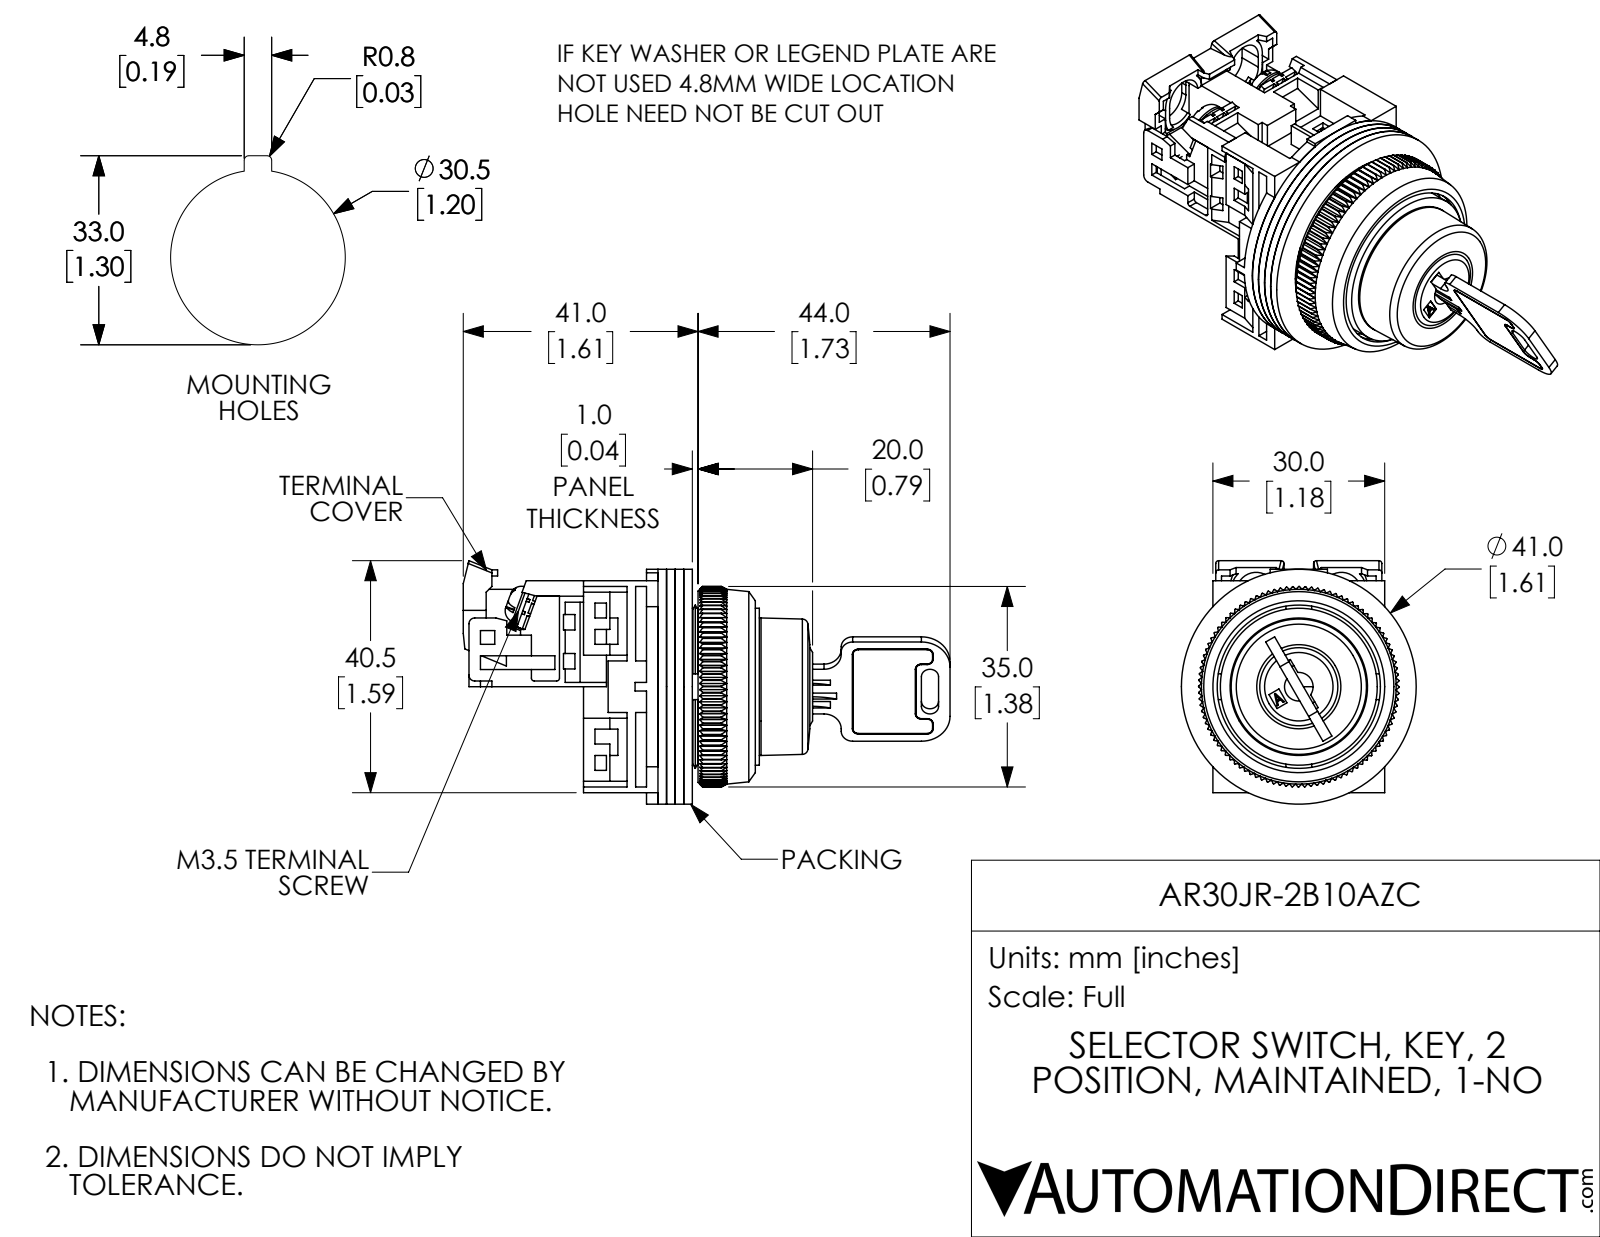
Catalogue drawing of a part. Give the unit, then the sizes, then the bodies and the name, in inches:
Units: inches
Overall size (bounding box): 3.346 × 1.673 × 1.614
Round holes (diameter × count): ⌀0.138 ×4, ⌀0.142 ×2, ⌀0.118 ×1, ⌀0.709 ×1, ⌀0.945 ×1, ⌀1.122 ×1, ⌀1.181 ×1, ⌀1.252 ×1
Round bosses / shafts (diameter × count): ⌀0.26 ×2, ⌀0.138 ×2, ⌀1.614 ×1, ⌀1.15 ×1, ⌀1.079 ×1
Partial cylindrical surfaces — rounded edges, fillets, slot ends (radius × count): R0.059 ×10, R0.02 ×6, R0.008 ×4, R0.039 ×3, R0.118 ×3, R0.079 ×2, R0.138 ×2, R0.177 ×2
Main face-to-face distances: 0.059, 0.118, 0.079, 0.039, 0.177, 0.197, 0.138, 0.256, 0.315, 0.689
Hole centre spacings: 0.579, 0.61
Volume: 1.964 in³ · Surface area: 45.39 in²
Bodies: 16 solids, 1404 faces (938 planar, 218 cylindrical, 248 other)
Part name (STEP PRODUCT): AR30JR-2B10AZC
STEP written by: SolidWorks 2017 (AUTOMOTIVE_DESIGN)
